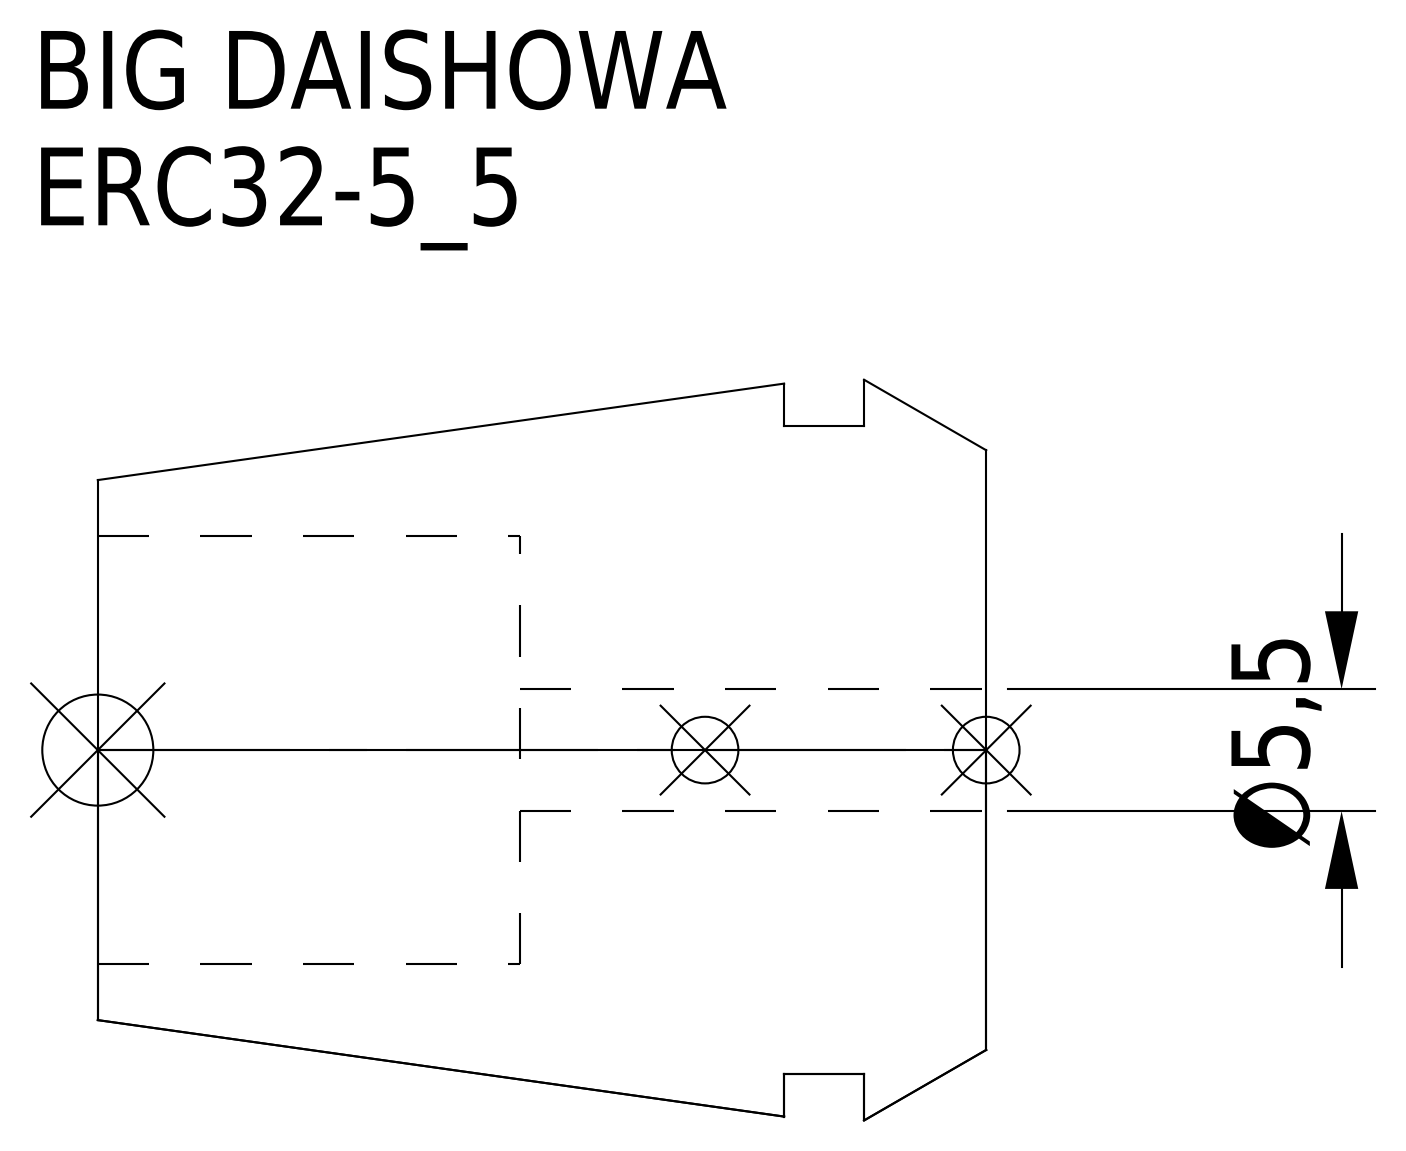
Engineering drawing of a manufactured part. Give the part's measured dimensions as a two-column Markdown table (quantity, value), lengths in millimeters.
| quantity | value |
| --- | --- |
| part name | ERC32-5_5 |
| STEP written by | CREO PARAMETRIC BY PTC INC, 2016380 (AUTOMOTIVE_DESIGN) |
| units | millimeters |
| bodies | 1 solid, 15 faces (5 planar, 6 cylindrical, 4 other) |
| overall size | 40 × 33.35 × 33.35 |
| volume | 20 385 mm³ |
| surface area | 6 635 mm² |
| round holes (diameter × count) | 5.5 × 1, 19.3 × 1 |
| round bosses / shafts (diameter × count) | 29.2 × 1 |
| main face-to-face distances | 21, 5.5, 15.5, 9.1, 3.6, 11.9, 40, 34.5, 30.9, 19 |
